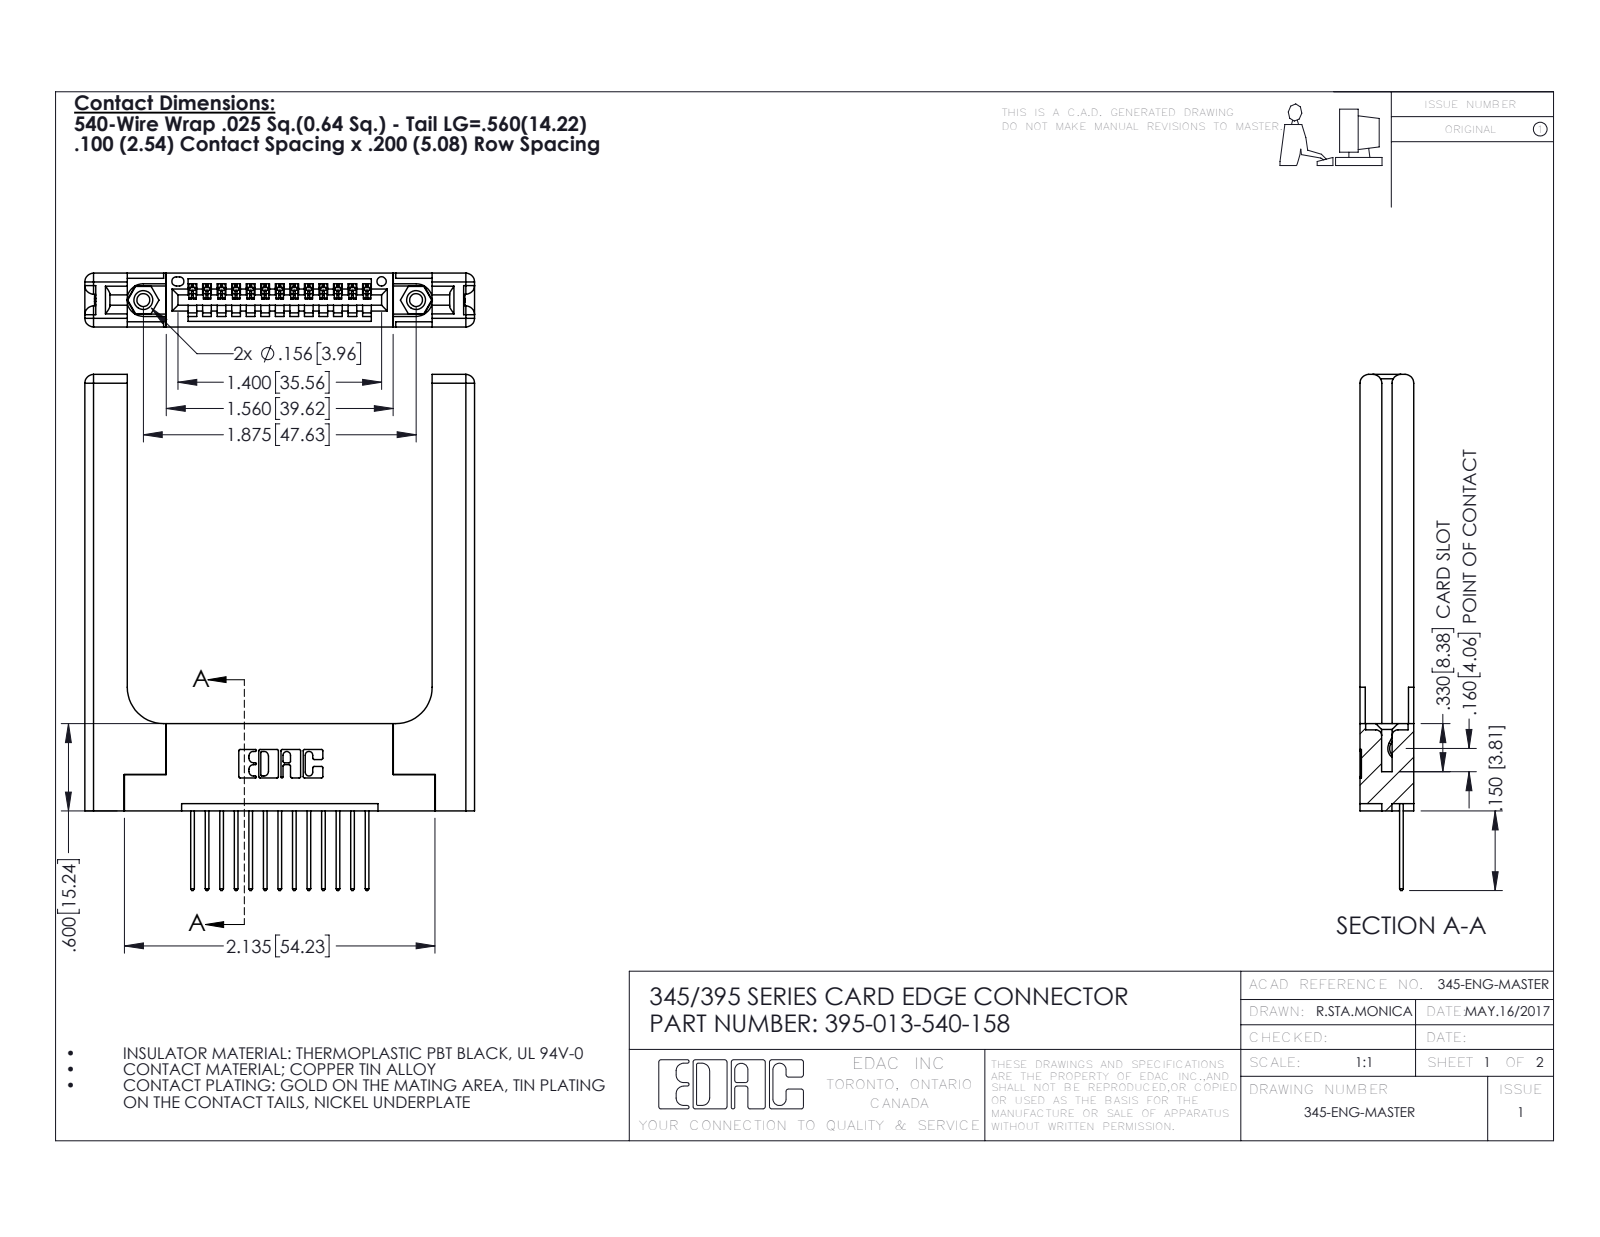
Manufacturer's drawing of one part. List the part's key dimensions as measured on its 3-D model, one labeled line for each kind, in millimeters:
Part name (STEP PRODUCT): 345 Part_Flush Mounting Lugs - 0.156 Dia-TH; 395-013-540-158; 345-250-001_345-250-001-102; 345-220-058_345-220-058 (+1 more)
STEP written by: SolidWorks 2016 (CONFIG_CONTROL_DESIGN)
Units: millimetres
Bodies: 18 solids, 1136 faces (748 planar, 328 cylindrical, 60 other)
Overall size (bounding box): 90.1 × 68 × 9.4
Volume: 14 700 mm³ · Surface area: 13 340 mm²
Round holes (diameter × count): ⌀2.3 ×2, ⌀3.2 ×2, ⌀4 ×2, ⌀1.6 ×1
Round bosses / shafts (diameter × count): ⌀3.9 ×2
Partial cylindrical surfaces — rounded edges, fillets, slot ends (radius × count): R0.2 ×26, R0.3 ×26, R0.3 ×22, R1.5 ×16, R0.2 ×6, R0.8 ×6, R0.7 ×3, R0.8 ×2
Main face-to-face distances: 9.4, 1.8, 7.6, 3.8, 2, 3.8, 5.6, 5.1, 2.5, 6.9
Hole centre spacings: 6.9, 41.7, 47.6
